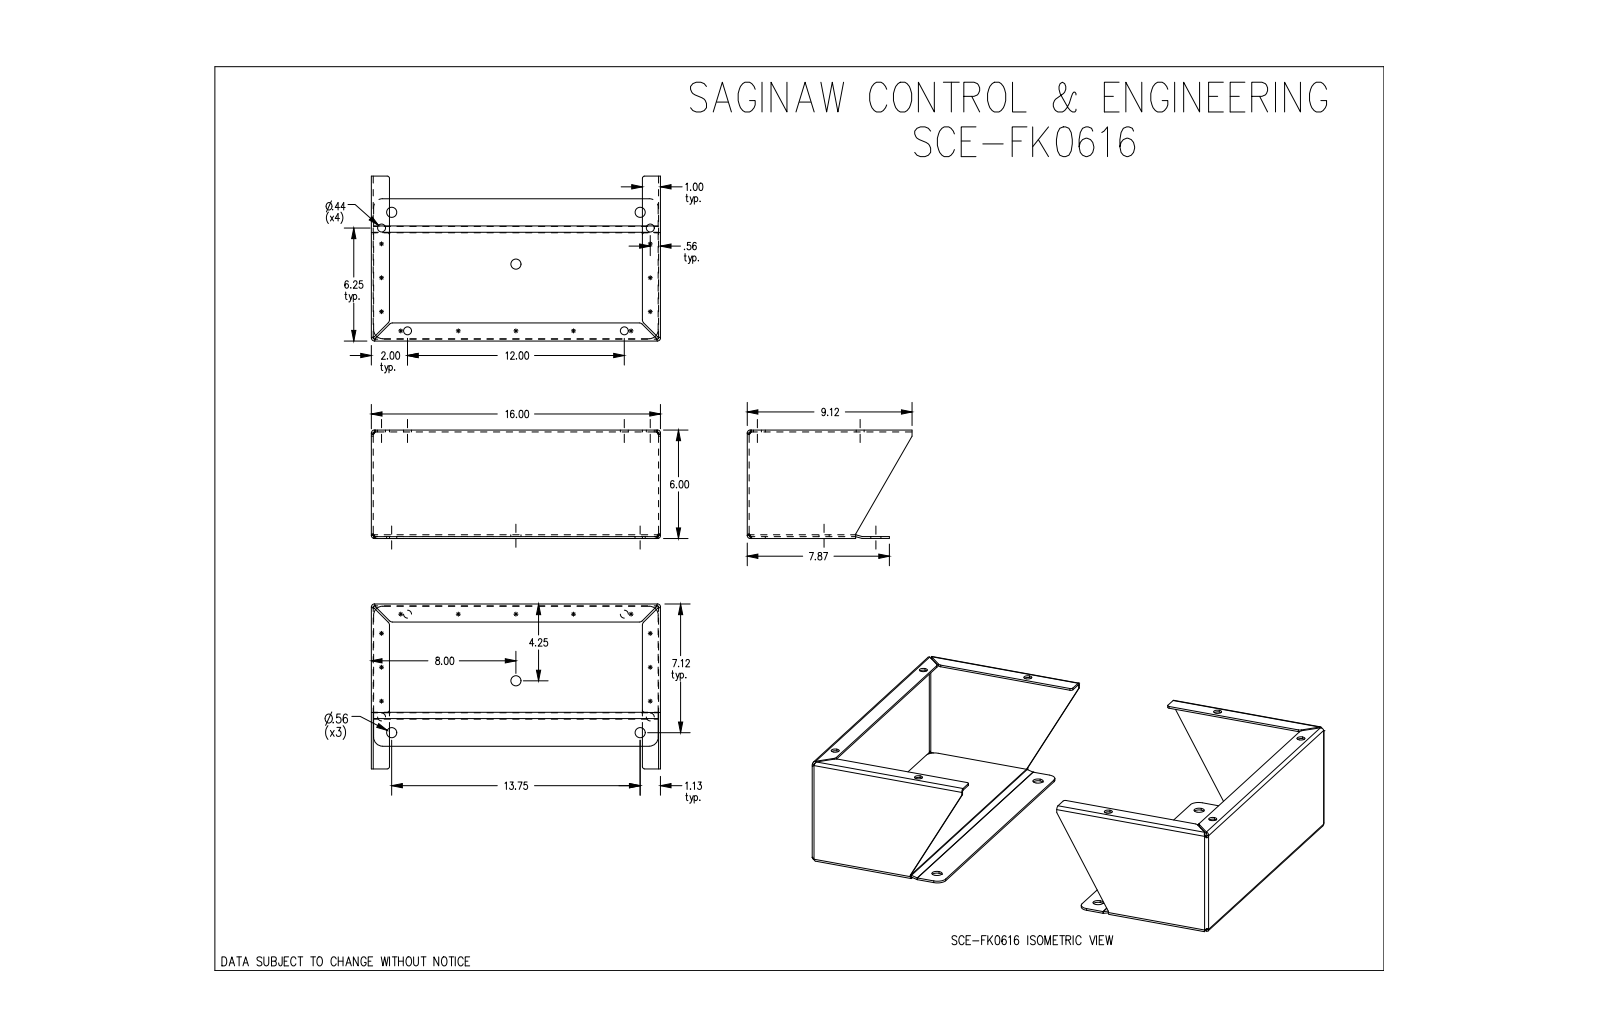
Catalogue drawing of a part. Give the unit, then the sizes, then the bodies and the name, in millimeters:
Units: millimetres
Overall size (bounding box): 609.6 × 406.4 × 152.4
Round holes (diameter × count): ⌀11.1 ×8, ⌀14.3 ×6
Partial cylindrical surfaces — rounded edges, fillets, slot ends (radius × count): R4.2 ×16, R1.6 ×14, R3.2 ×8, R5.6 ×8, R12.7 ×8, R1.6 ×2
Main face-to-face distances: 2.6, 607, 403.8, 147.1, 149.8, 2.6, 149.7, 609.6, 604.3, 401.1
Hole centre spacings: 26.3, 149, 168, 178.9, 189.2, 195.6, 270.4, 365.3
Volume: 1 206 000 mm³ · Surface area: 931 600 mm²
Bodies: 4 solids, 214 faces (96 planar, 86 cylindrical, 32 other)
Part name (STEP PRODUCT): SCE-FK0616
STEP written by: SolidWorks 2019 (CONFIG_CONTROL_DESIGN)
